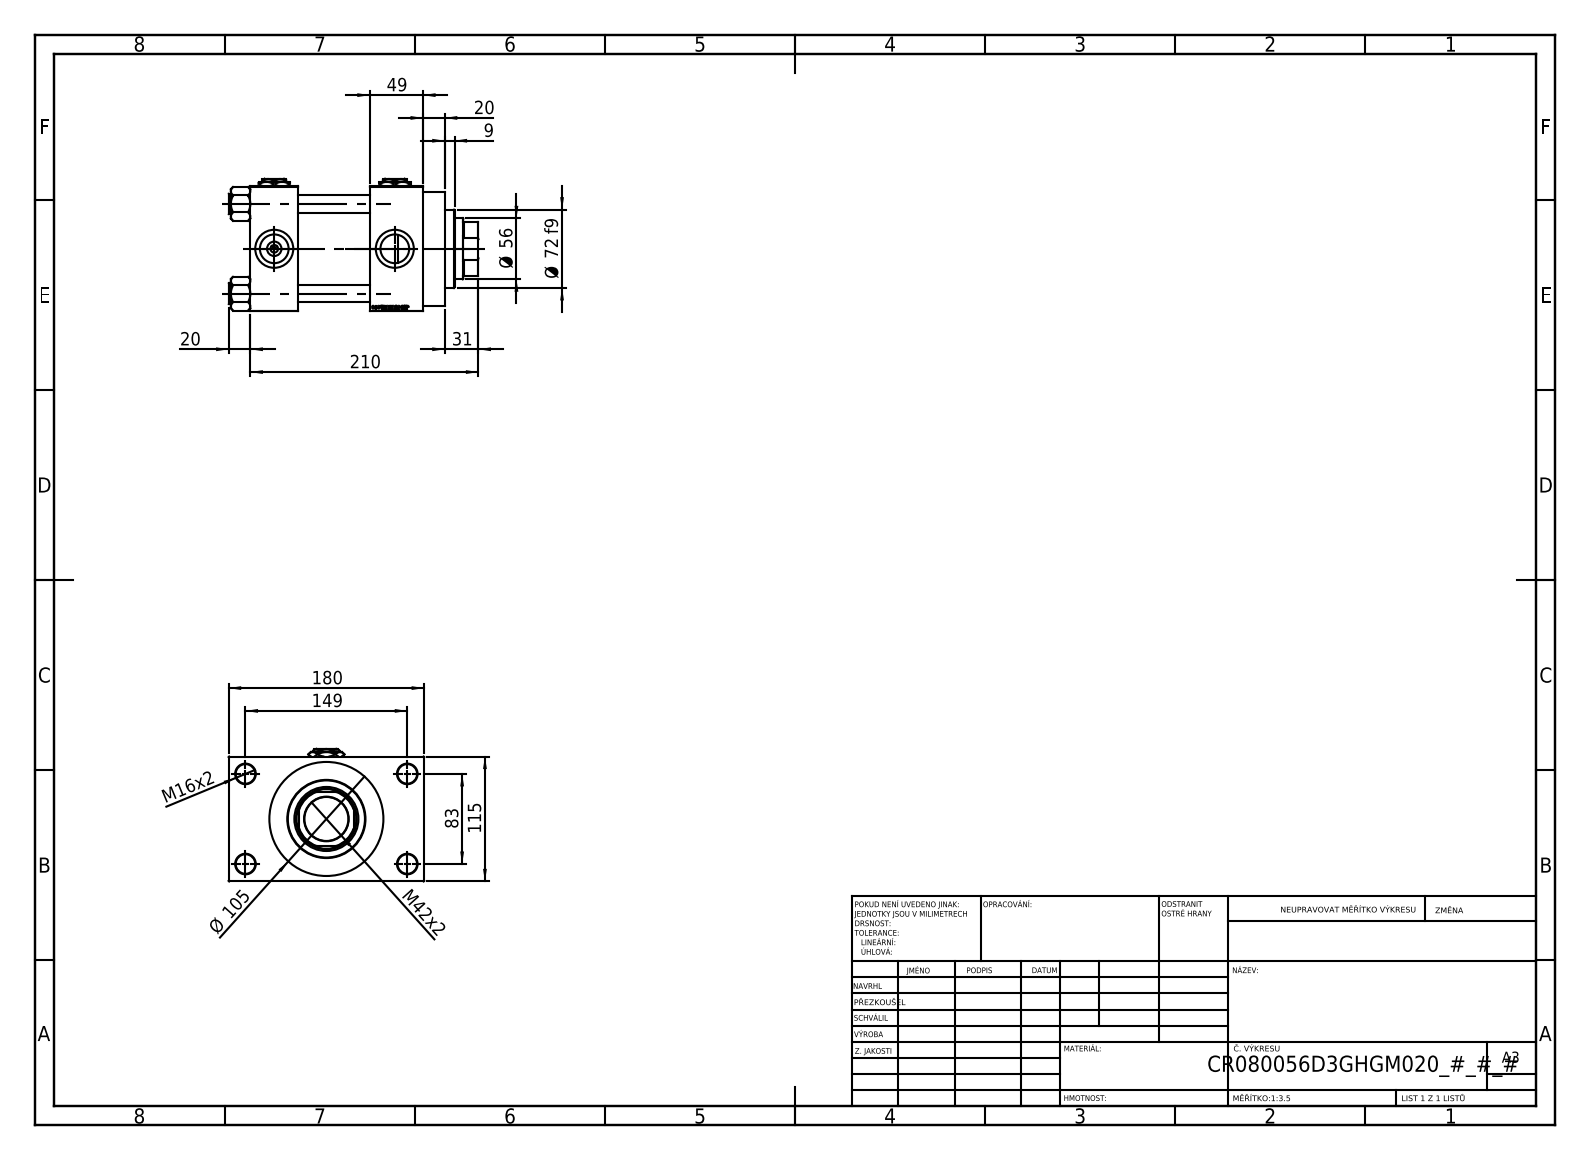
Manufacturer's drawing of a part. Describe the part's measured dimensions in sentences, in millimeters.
The part is named "V215CR_VCP_D; NUT_M5_D; V215CR_D_Body; V215_VC_A (+2 more)". Its 3-D file was written by "SolidWorks 2019 (CONFIG_CONTROL_DESIGN)". It is 13 solids with 1249 faces: 592 planar, 97 cylindrical and 560 other. Overall it measures 230 by 180 by 122 millimeters. Its volume is 2 088 000 cubic millimeters and its surface area 317 447 square millimeters. Round holes: 4 of diameter 16, 4 of diameter 18, 4 of diameter 26.44, 4 of diameter 35, 3 of diameter 7, 1 of diameter 40.5, 1 of diameter 56, 1 of diameter 59, 1 of diameter 61, 1 of diameter 72, 1 of diameter 80. Round bosses or shafts: 4 of diameter 19, 1 of diameter 105, 1 of diameter 86. Partial cylindrical surfaces (rounded edges, fillets, slot ends): 1 of radius 27. The main face-to-face distances are 115, 66, 110, 44, 159, 49, 32.5, 147.5, 20, 69. The hole center spacings are 33.15, 58.48, 82.7, 85.28, 89.24, 115.85, 142.43, 83.
